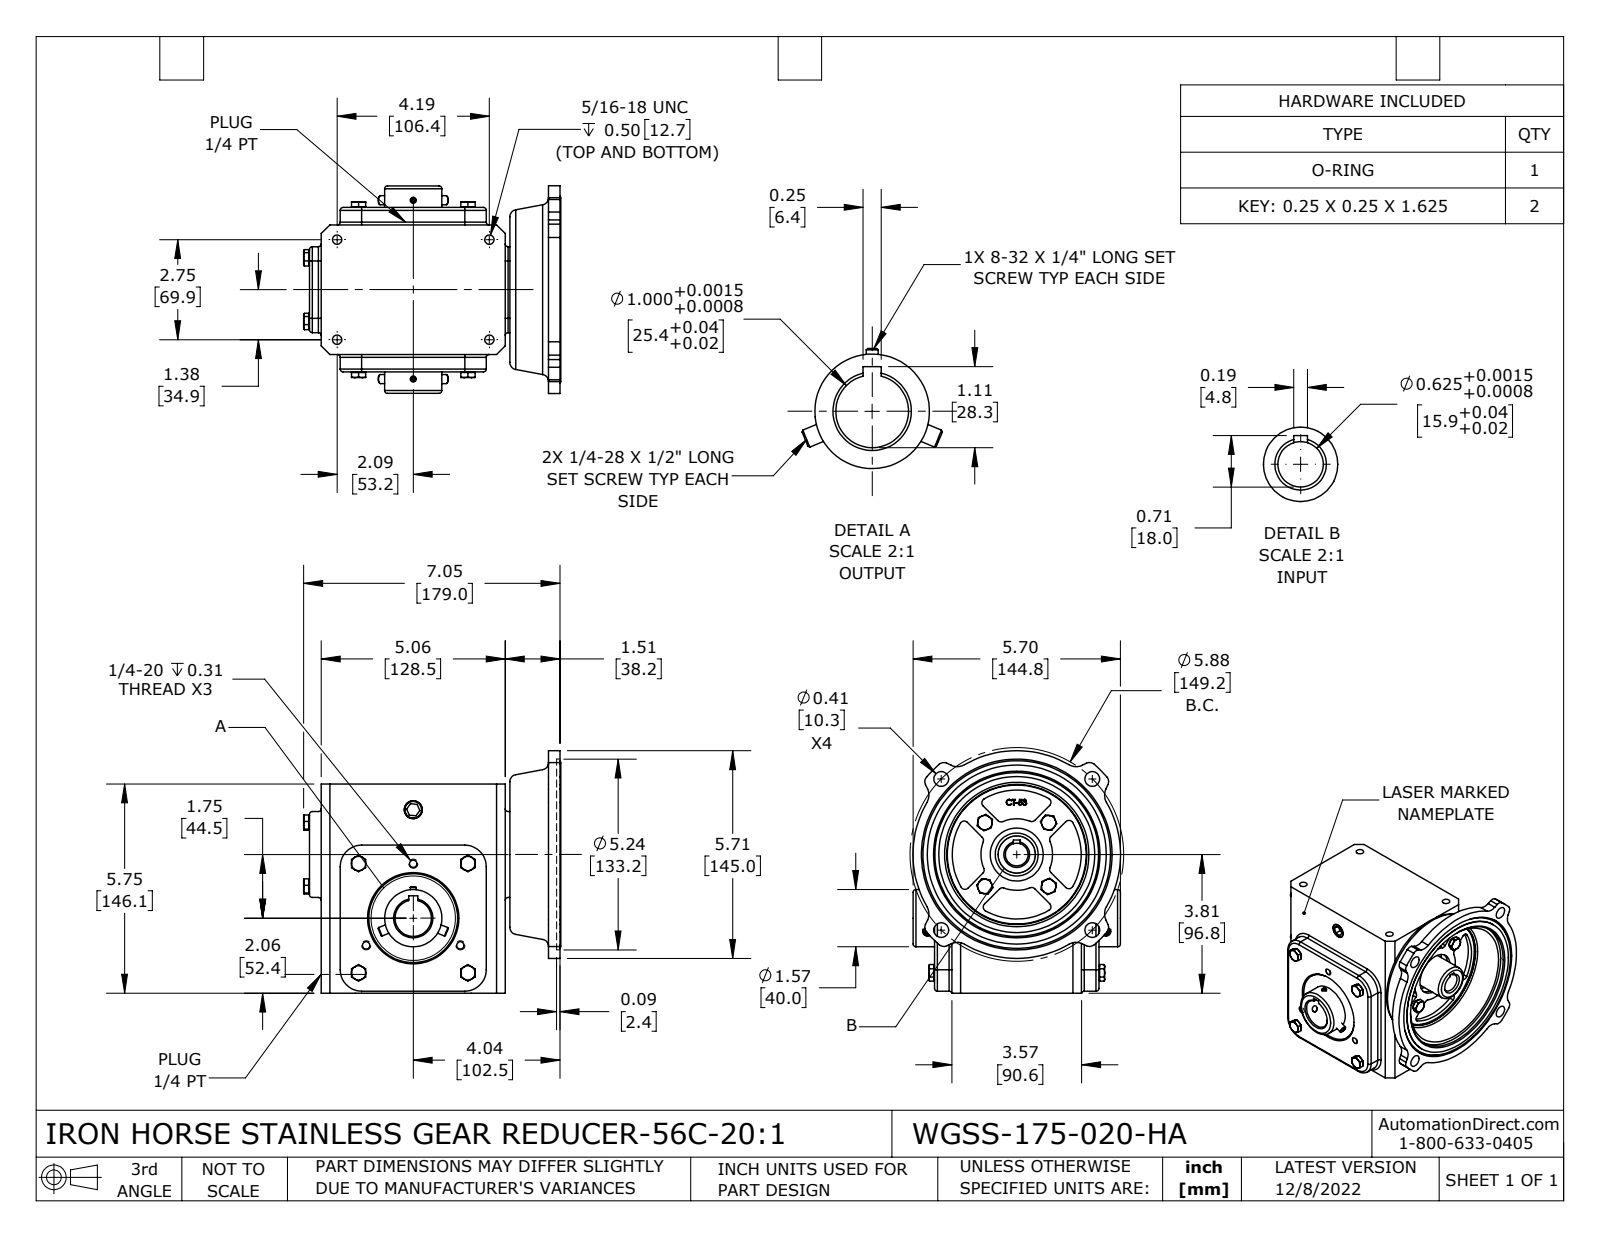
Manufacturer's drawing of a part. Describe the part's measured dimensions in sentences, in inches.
The part is named "WGSS-175-020-HA". Its 3-D file was written by "SolidWorks 2021 (CONFIG_CONTROL_DESIGN)". It is 7 solids with 891 faces: 390 planar, 231 cylindrical and 270 other. Overall it measures 7.071 by 6.691 by 5.709 inches. Its volume is 127 cubic inches and its surface area 281 square inches. Round holes: 4 of diameter 0.213, 4 of diameter 0.257, 4 of diameter 0.406, 3 of diameter 0.201, 2 of diameter 0.136, 1 of diameter 0.625, 1 of diameter 0.866, 1 of diameter 1, 1 of diameter 1.102, 1 of diameter 1.457, 1 of diameter 1.575, 1 of diameter 3.819. Round bosses or shafts: 8 of diameter 0.394, 4 of diameter 0.25, 2 of diameter 0.164, 1 of diameter 4.921, 1 of diameter 2.441, 1 of diameter 1.575, 1 of diameter 1.181. Partial cylindrical surfaces (rounded edges, fillets, slot ends): 28 of radius 0.079, 16 of radius 0.118, 12 of radius 0.394, 8 of radius 0.197, 4 of radius 0.591, 1 of radius 0.984, 1 of radius 1.772, 1 of radius 2.854. The main face-to-face distances are 0.48, 4.04, 5.75, 5.06, 0.157, 3.56, 4.52, 0.315, 6.565, 1.506. The hole center spacings are 2.357, 2.937, 4.154, 1.496, 2.591, 4.913, 2.75, 4.188.
